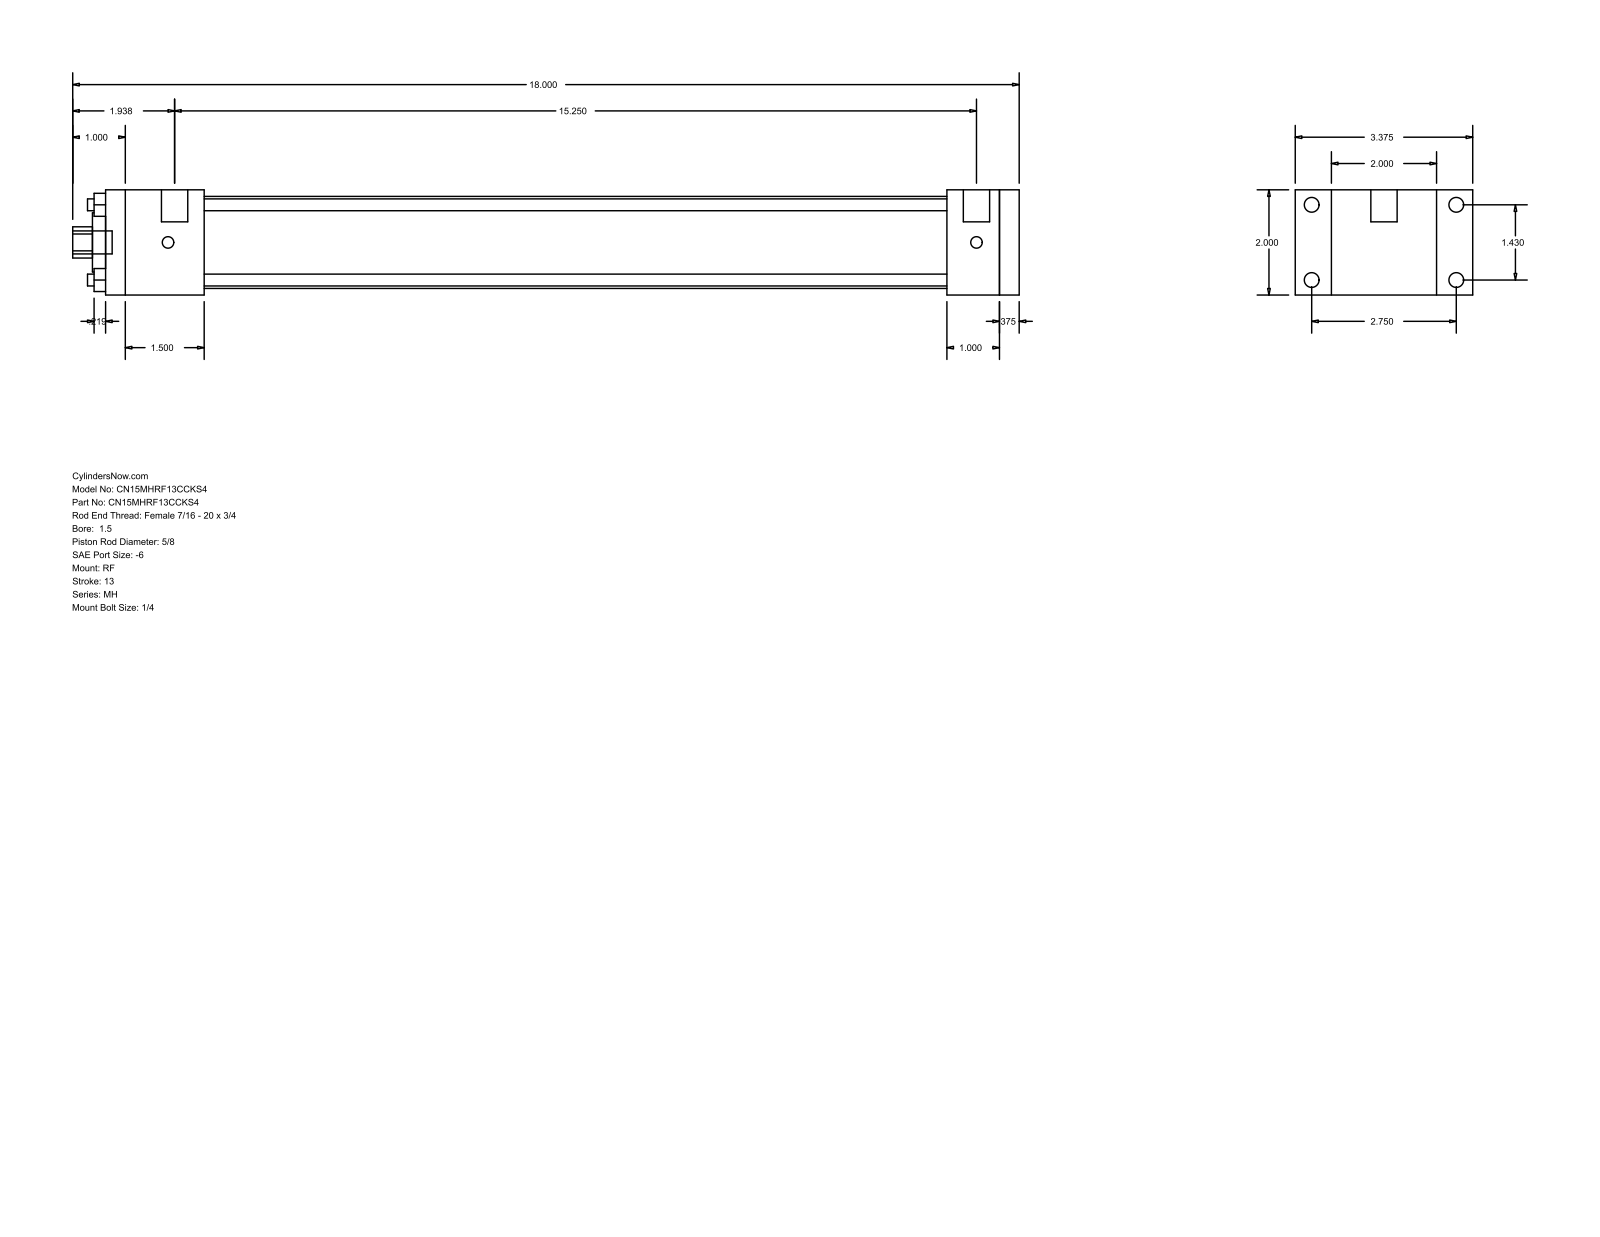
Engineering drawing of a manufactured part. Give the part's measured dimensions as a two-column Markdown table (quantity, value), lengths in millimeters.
| quantity | value |
| --- | --- |
| part name | MH_RF__0150_0.625 |
| STEP written by | GSSL Pune (CONFIG_CONTROL_DESIGN) |
| units | millimeters |
| bodies | 0 solids, 92 faces (64 planar, 28 cylindrical, 0 other) |
| overall size | 457.2 × 85.72 × 50.8 |
| round holes (diameter × count) | 5.71 × 4, 15.88 × 1, 28.57 × 1, 44.45 × 1 |
| round bosses / shafts (diameter × count) | 7.14 × 4, 5.56 × 4, 12.7 × 2, 11.11 × 1 |
| partial cylindrical surfaces (radius × count) | 7.54 × 1 |
| main face-to-face distances | 50.8, 9.52, 431.8, 441.32, 17.46, 68.26, 406.39, 25.41, 34.93, 47.62 |
| hole center spacings | 25.68, 36.32, 51.36 |
